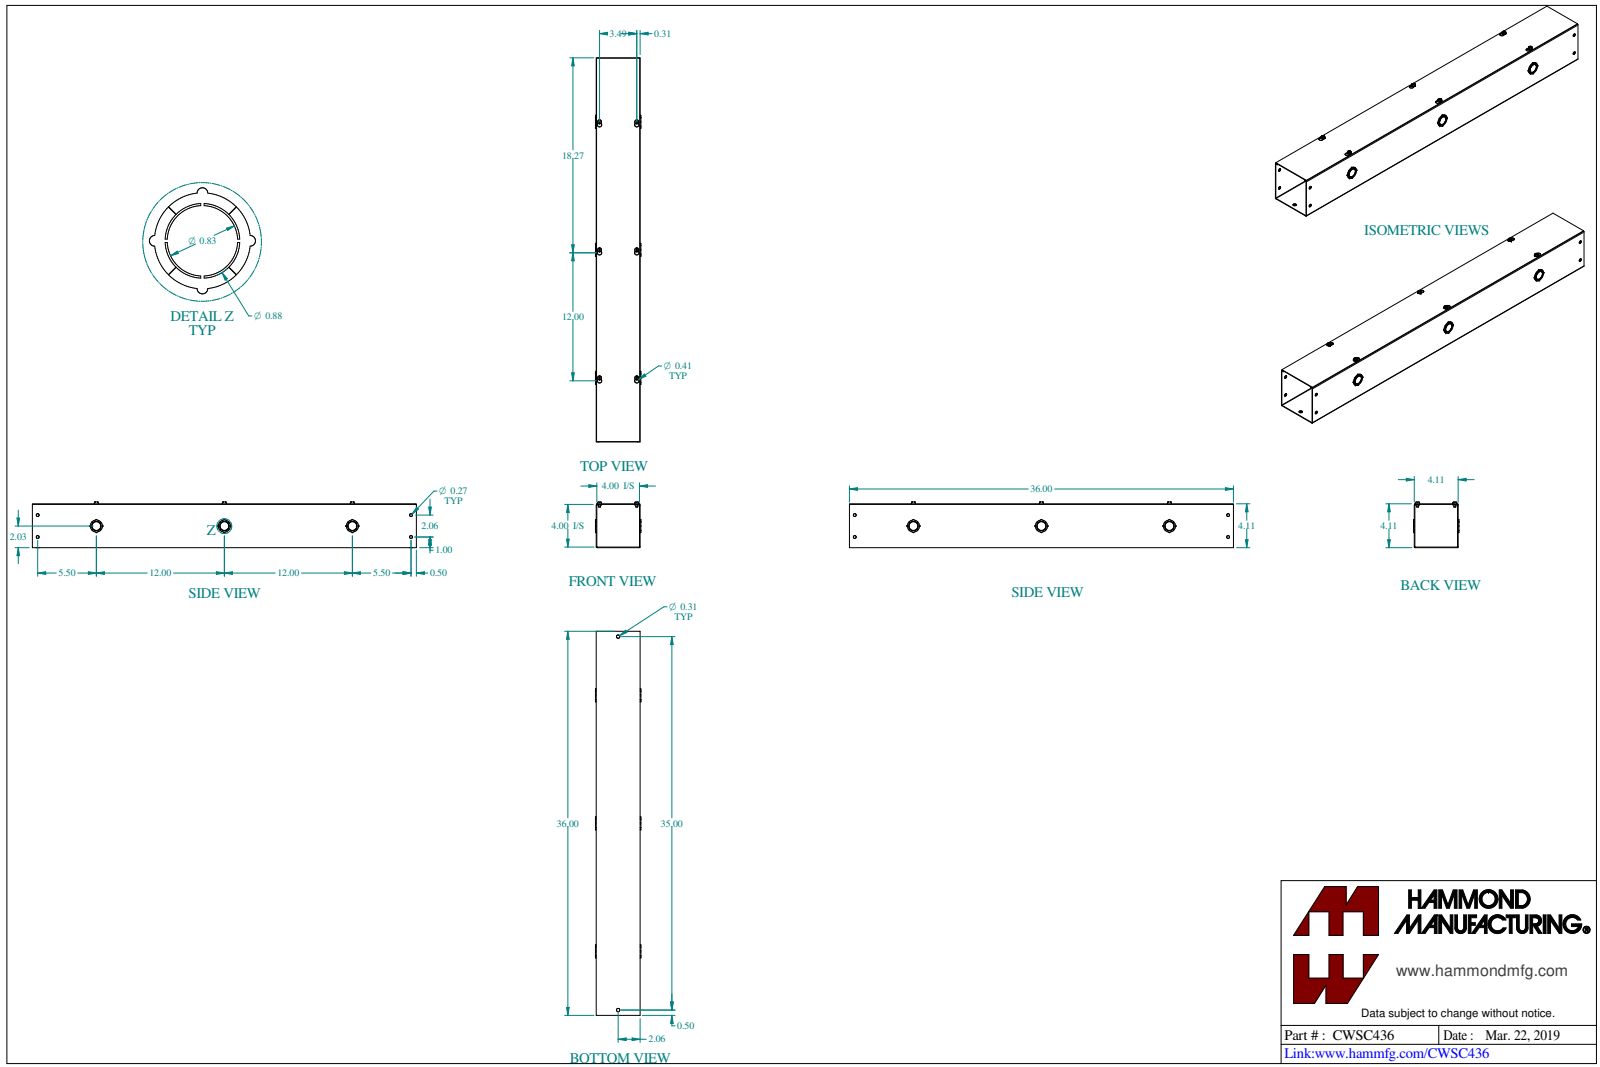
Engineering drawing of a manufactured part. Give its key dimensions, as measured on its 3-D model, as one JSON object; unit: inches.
{"part_name": "CWSC436", "step_written_by": "SolidWorks 2023 (CONFIG_CONTROL_DESIGN)", "units": "inches", "bodies": {"solids": 8, "faces": 494, "planar": 220, "cylindrical": 238, "other": 36}, "overall_size": [36, 4.289, 4.258], "volume_in3": 35.17, "surface_area_in2": 1234, "round_holes": [[0.177, 6], [0.266, 4], [0.875, 3], [0.313, 2]], "round_bosses_or_shafts": [[0.375, 6], [0.19, 6], [1.125, 3], [1.125, 3], [0.825, 3]], "partial_cylinders_radius": [[0.062, 9], [0.125, 6], [0.203, 6], [0.029, 4], [0.086, 4], [0.063, 3]], "face_to_face_distances": [0.057, 4.057, 4, 4.114, 3.943, 0.114, 0.072, 0.129, 4.129, 4.186], "hole_center_spacings": [12, 5.595, 5.77, 12.497, 17.53, 17.587, 29.518, 29.552]}
